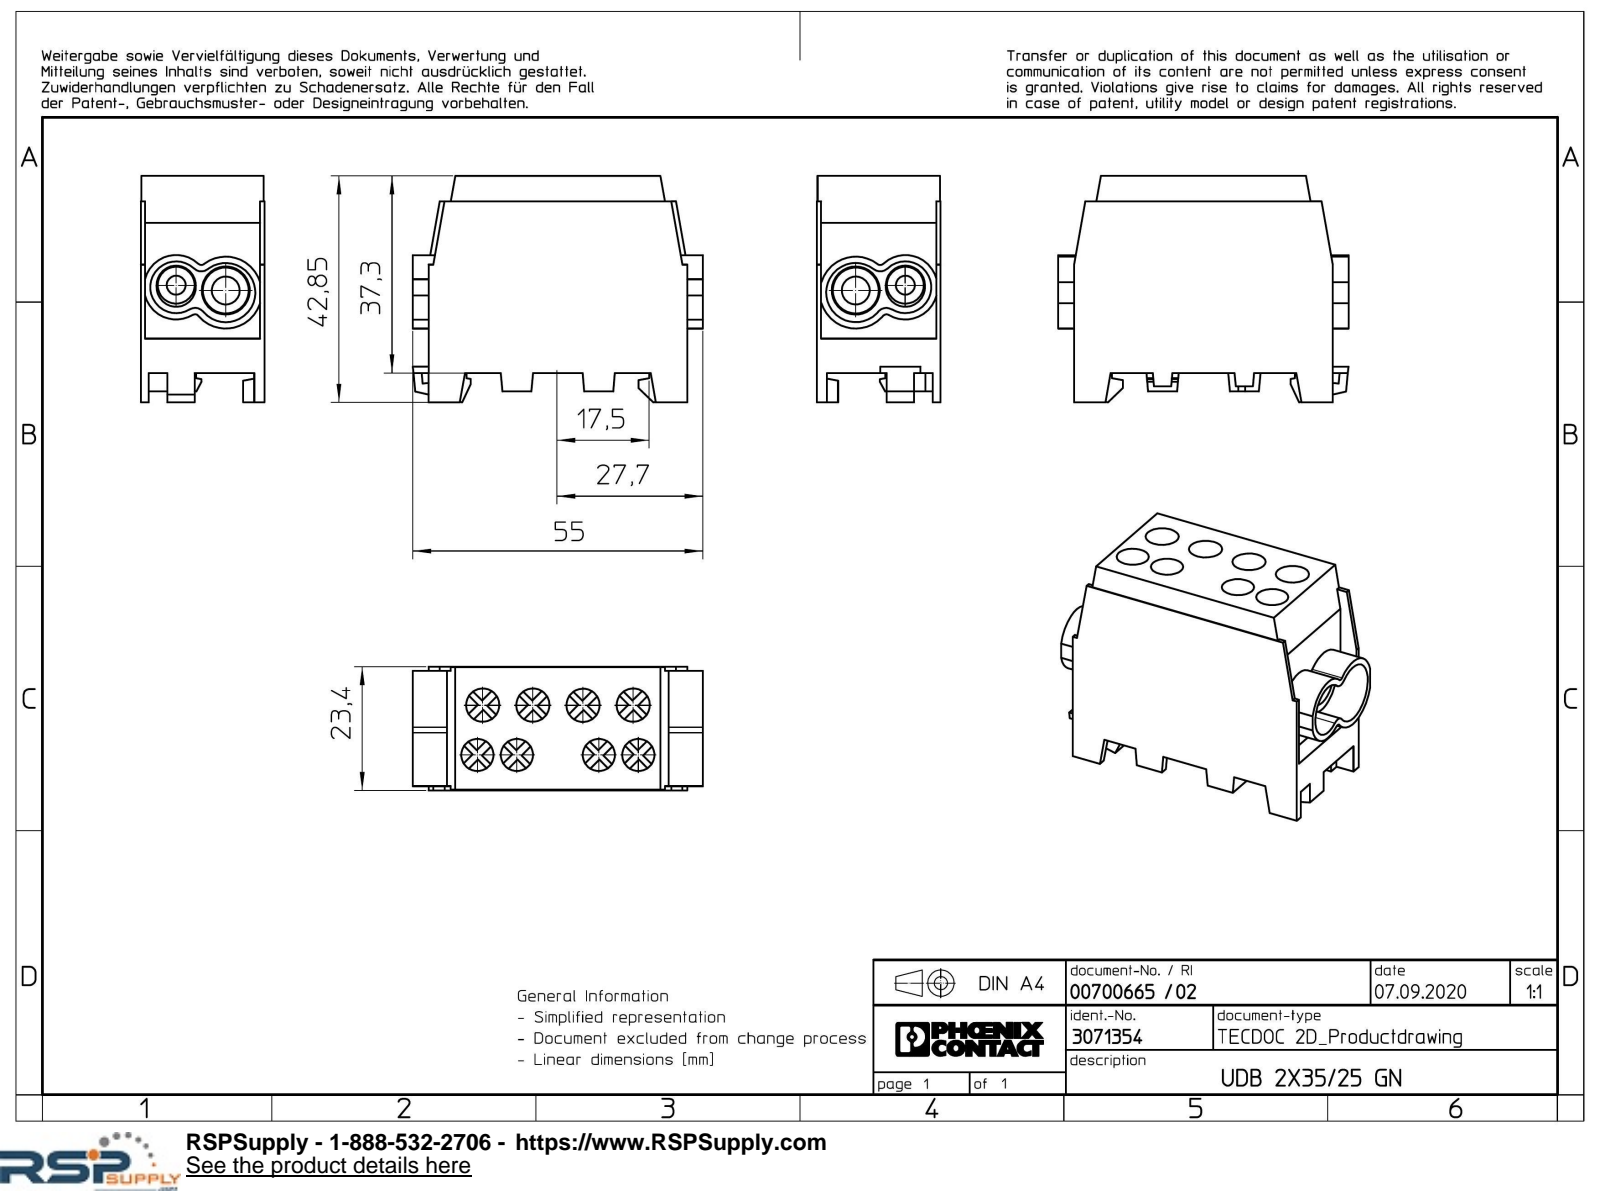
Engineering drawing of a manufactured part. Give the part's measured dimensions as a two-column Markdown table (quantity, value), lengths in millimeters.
| quantity | value |
| --- | --- |
| part name | UDB_2x35_25_GN-select |
| STEP written by | Creo Elements/Direct Modeling 20.1A 29-Sep-2018 (C) Parametric Technology GmbH (AUTOMOTIVE_DESIGN) |
| units | millimeters |
| bodies | 1 solid, 275 faces (209 planar, 52 cylindrical, 14 other) |
| overall size | 55 × 42.85 × 23.4 |
| volume | 33 976 mm³ |
| surface area | 13 197 mm² |
| round holes (diameter × count) | 6.1 × 4, 6.3 × 4, 7 × 1, 8.7 × 1, 9.1 × 1 |
| partial cylindrical surfaces (radius × count) | 0.8 × 2, 2 × 2, 3.7 × 2, 4.9 × 1, 5.6 × 1, 6.1 × 1, 6.8 × 1 |
| main face-to-face distances | 23.4, 37.3, 3.5, 45.5, 23.3, 0.7, 0.8, 6.5, 22.6, 22.5 |
| hole center spacings | 9.45, 7.5, 11.43, 15.64, 22.1, 23, 23.92, 30.96 |
